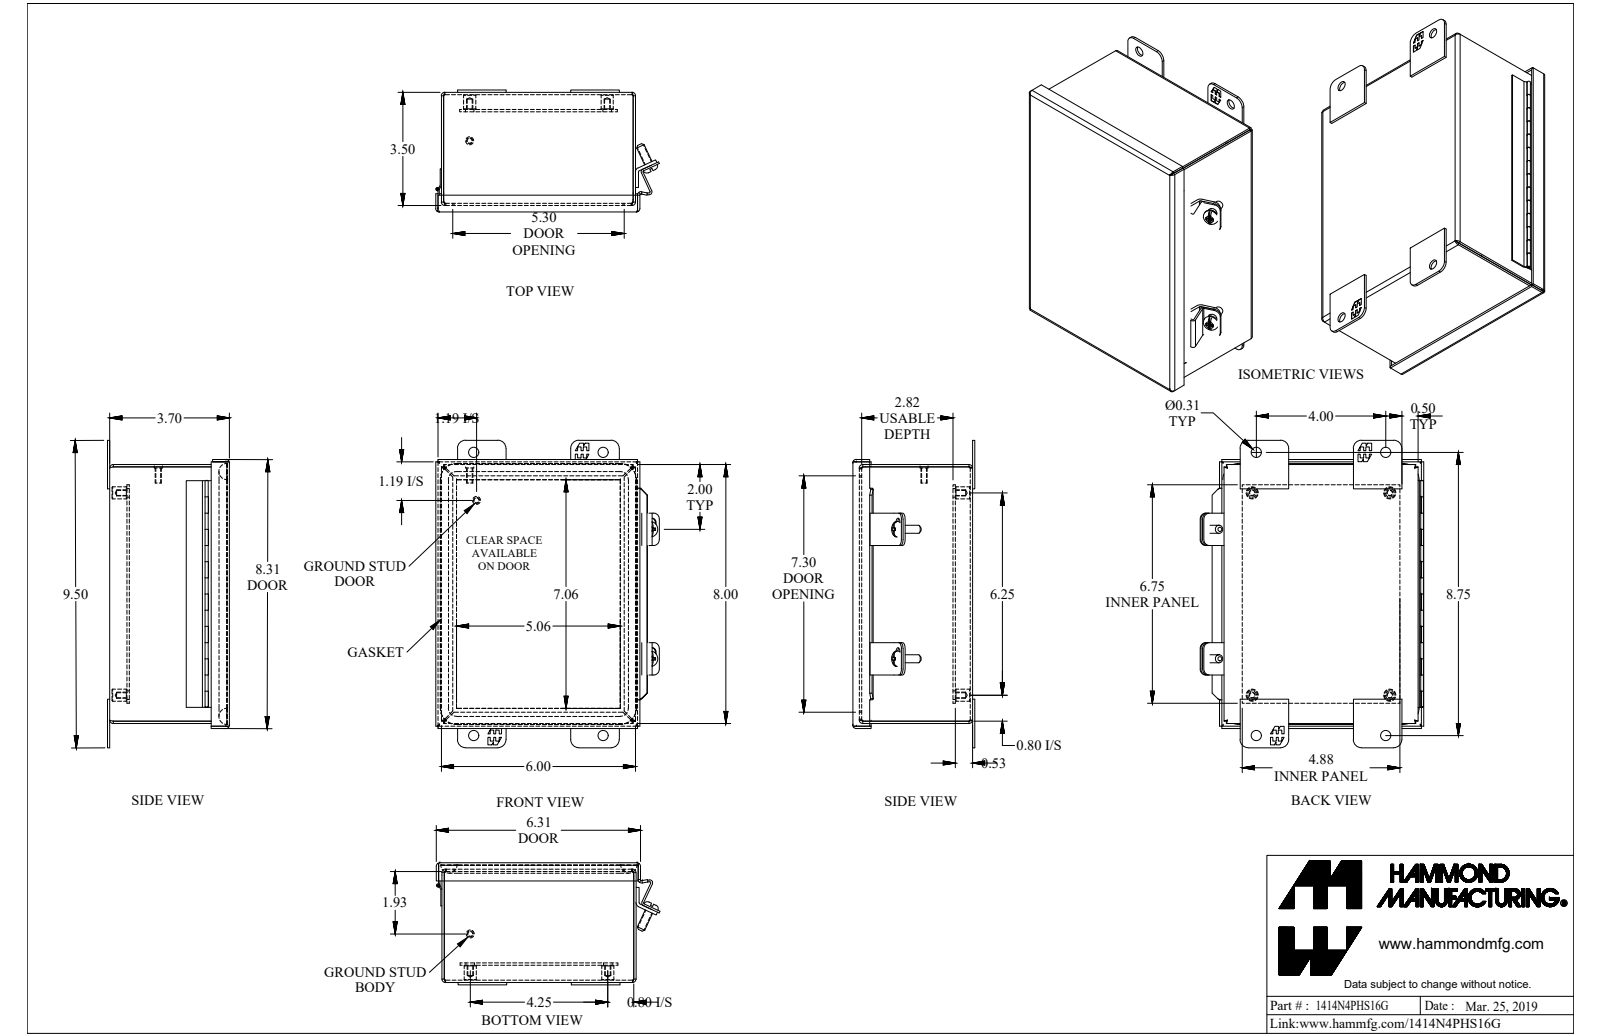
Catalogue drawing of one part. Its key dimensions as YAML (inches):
part_name: "1414N4PHS16G"
step_written_by: "SolidWorks 2018 (AUTOMOTIVE_DESIGN)"
units: inches
bodies: {solids: 21, faces: 653, planar: 427, cylindrical: 168, other: 58}
overall_size: [9.5, 6.903, 3.769]
volume: 22.62
surface_area: 622.1
round_holes:
  - {diameter: 0.156, count: 4}
  - {diameter: 0.265, count: 4}
  - {diameter: 0.313, count: 4}
  - {diameter: 0.213, count: 2}
  - {diameter: 0.05, count: 1}
round_bosses_or_shafts:
  - {diameter: 0.375, count: 4}
  - {diameter: 0.25, count: 4}
  - {diameter: 0.48, count: 2}
  - {diameter: 0.19, count: 2}
  - {diameter: 0.1, count: 1}
  - {diameter: 0.045, count: 1}
partial_cylinders:
  - {radius: 0.25, count: 24}
  - {radius: 0.036, count: 8}
  - {radius: 0.108, count: 8}
  - {radius: 0.188, count: 8}
  - {radius: 0.037, count: 4}
  - {radius: 0.079, count: 4}
  - {radius: 0.118, count: 4}
  - {radius: 0.141, count: 4}
face_to_face_distances: [0.072, 0.532, 0.081, 3.625, 3.697, 5.928, 3.616, 3.093, 3.544, 0.604]
hole_center_spacings: [1.256, 6.25, 7.501, 7.558, 8.559, 4, 4.31, 4.31]
